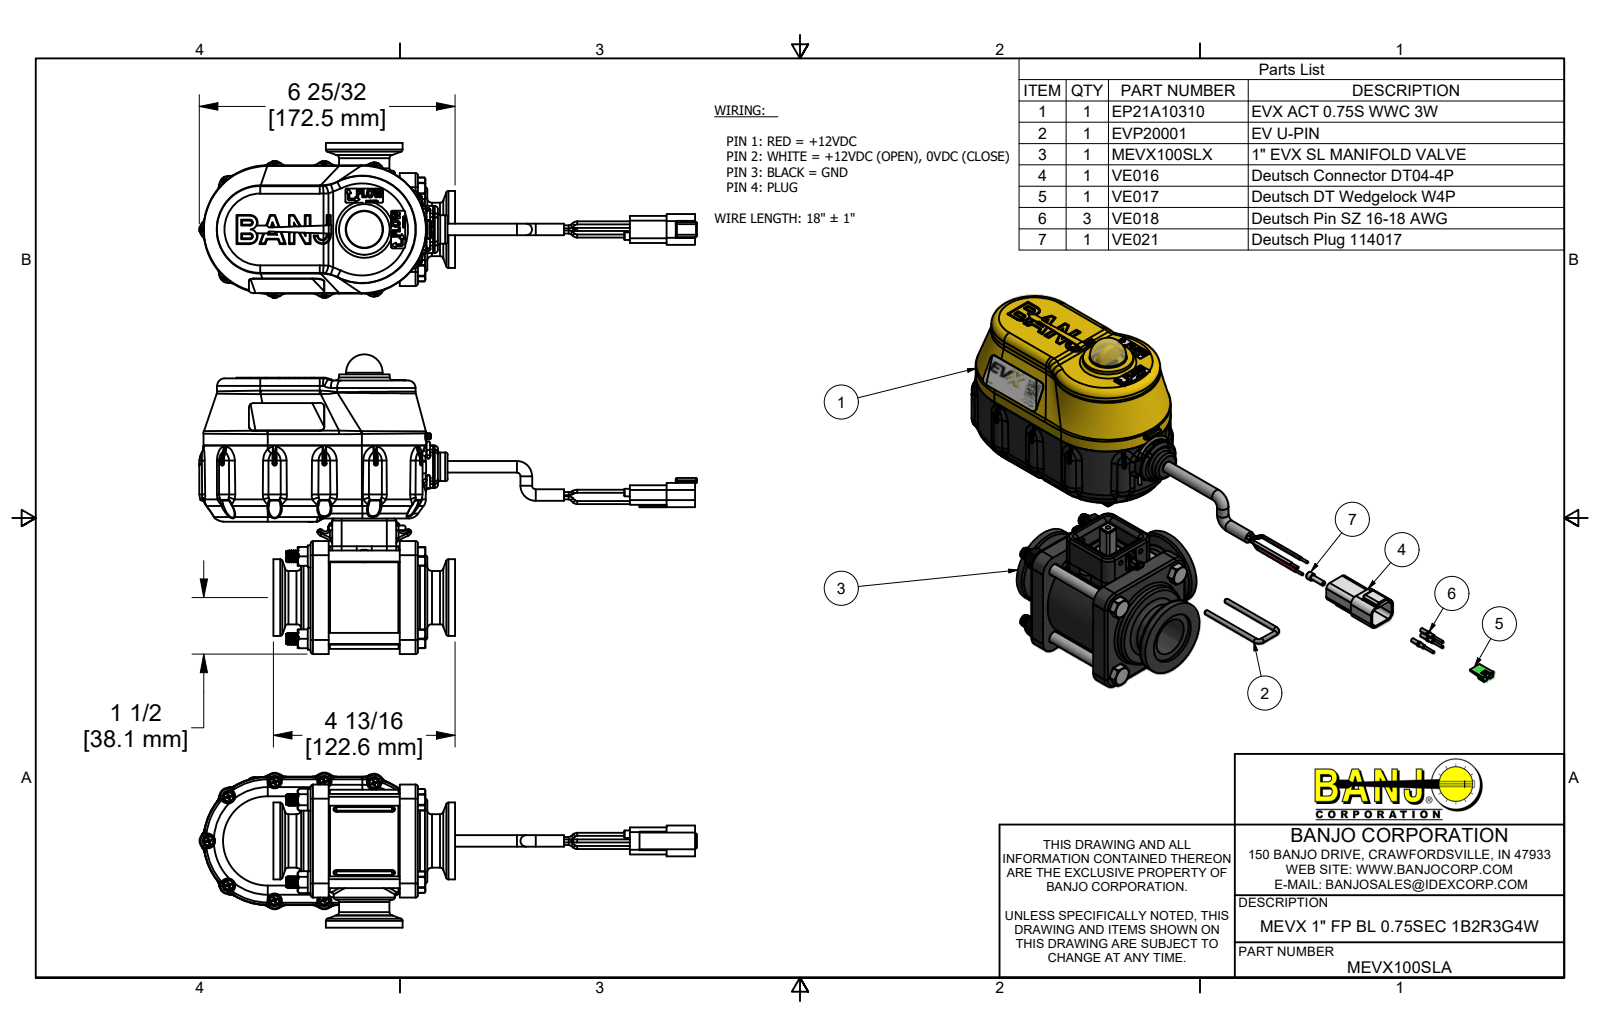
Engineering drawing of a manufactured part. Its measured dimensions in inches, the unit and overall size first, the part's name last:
Units: inches
Overall size (bounding box): 13.22 × 7.957 × 4.115
Round holes (diameter × count): ⌀0.095 ×11, ⌀0.15 ×11, ⌀0.15 ×8, ⌀0.08 ×7, ⌀0.03 ×4, ⌀0.107 ×4, ⌀0.126 ×4, ⌀0.136 ×4, ⌀0.148 ×4, ⌀0.17 ×4, ⌀0.252 ×4, ⌀0.322 ×4
Round bosses / shafts (diameter × count): ⌀0.268 ×60, ⌀0.25 ×17, ⌀0.08 ×15, ⌀0.14 ×11, ⌀0.108 ×11, ⌀0.085 ×11, ⌀0.058 ×6, ⌀0.313 ×5
Partial cylindrical surfaces — rounded edges, fillets, slot ends (radius × count): R0.013 ×180, R0.04 ×145, R0.01 ×84, R0.02 ×72, R0.005 ×53, R0.03 ×46, R0.06 ×44, R0.125 ×30
Main face-to-face distances: 0.1, 2.565, 0.48, 0.055, 0.211, 0.06, 0.151, 2.365, 0.125, 1.896
Hole centre spacings: 1.547, 2.188, 2.656, 0.165, 1.513, 1.662, 1.891, 2.69
Volume: 54.07 in³ · Surface area: 610.8 in²
Bodies: 104 solids, 12035 faces (3236 planar, 3529 cylindrical, 5270 other)
Part name (STEP PRODUCT): MEVX100SLA; MEVX100SLX; MEVX10354AS; MEVX10354ASX (+8 more)
STEP written by: Autodesk Inventor 2019 (AUTOMOTIVE_DESIGN)
